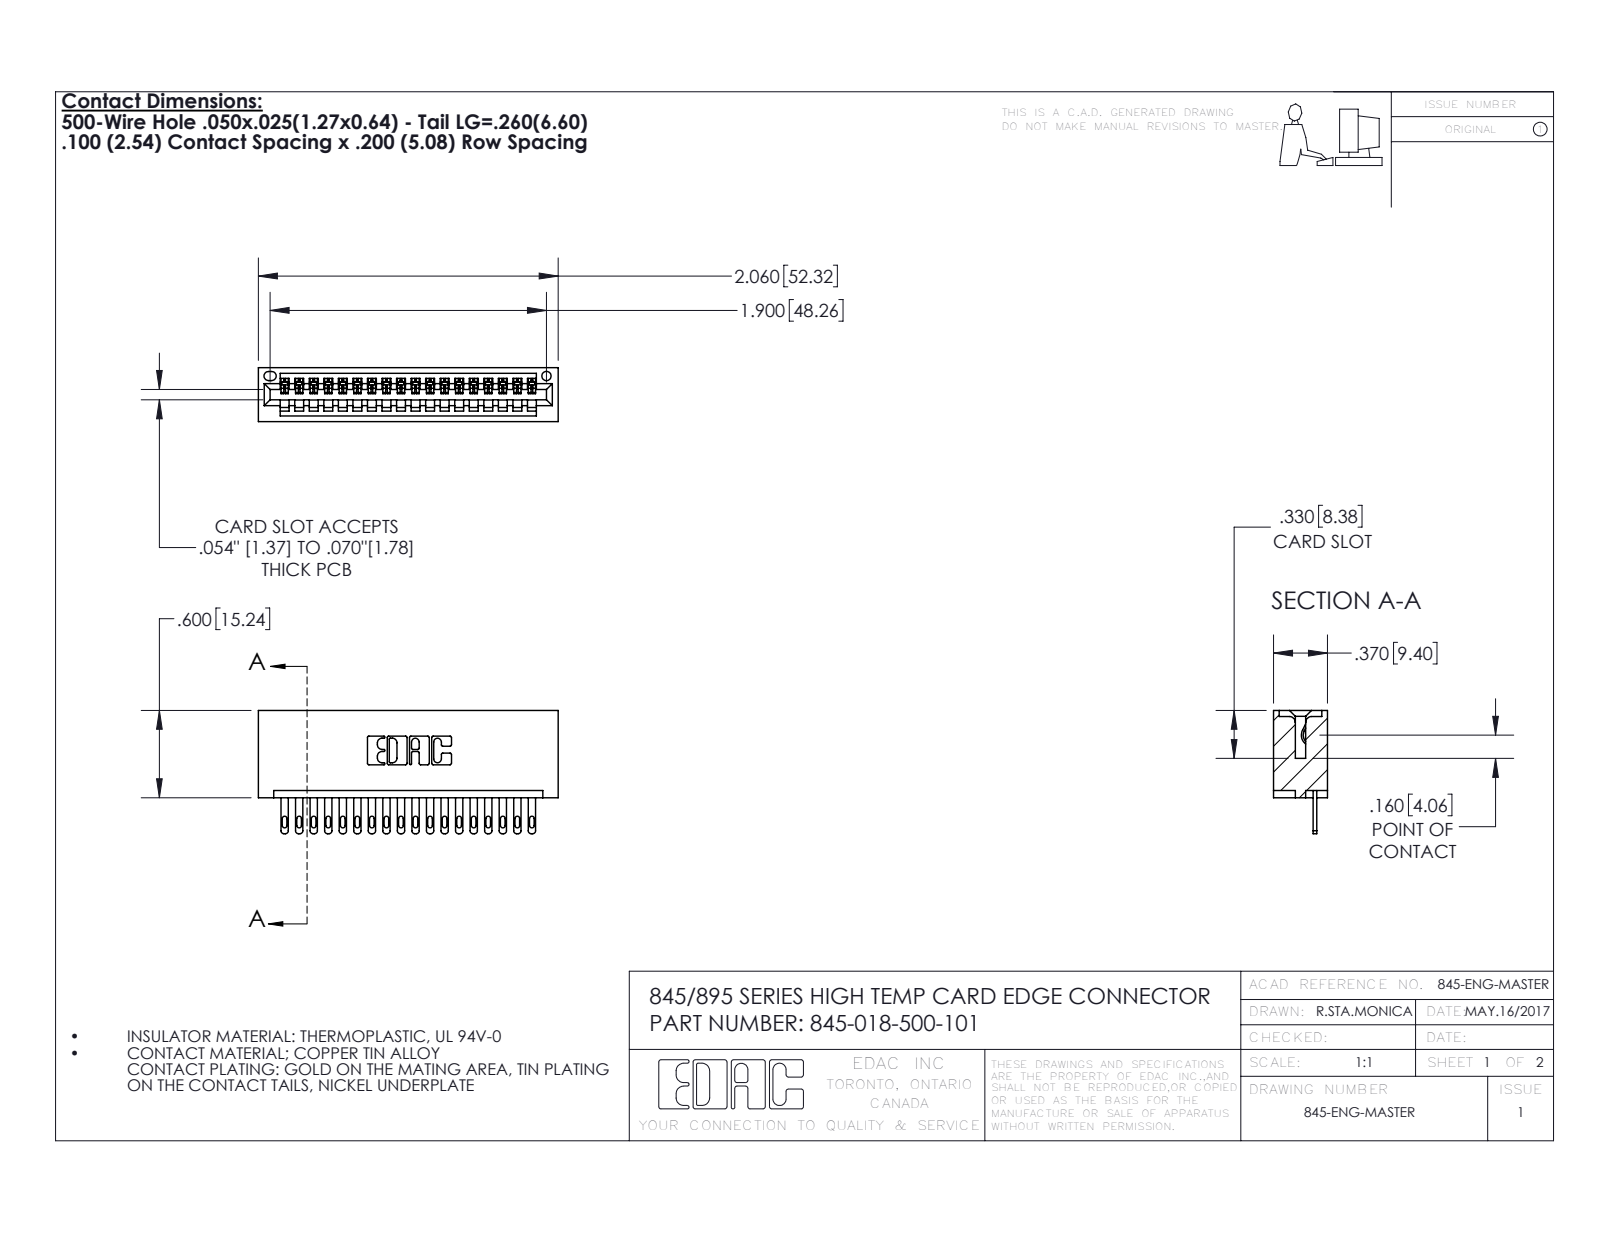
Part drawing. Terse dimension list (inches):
name: 345 Part_No Mounting Lugs; 345-292-001_345-293-100; 345-018-500-101
written by: SolidWorks 2016 (CONFIG_CONTROL_DESIGN)
unit: in
bodies: 19 solids, 1090 faces (688 planar, 402 cylindrical, 0 other)
size: 2.06 × 0.847 × 0.37
volume: 0.328 in³; area: 10.91 in²
holes: 1× ⌀0.064
rounds: 36× R0.006, 36× R0.016, 36× R0.02, 22× R0.01, 6× R0.007, 6× R0.031, 3× R0.026, 2× R0.031
face distances: 0.298, 0.072, 0.2, 0.37, 0.098, 0.272, 0.025, 0.1, 0.225, 0.3
